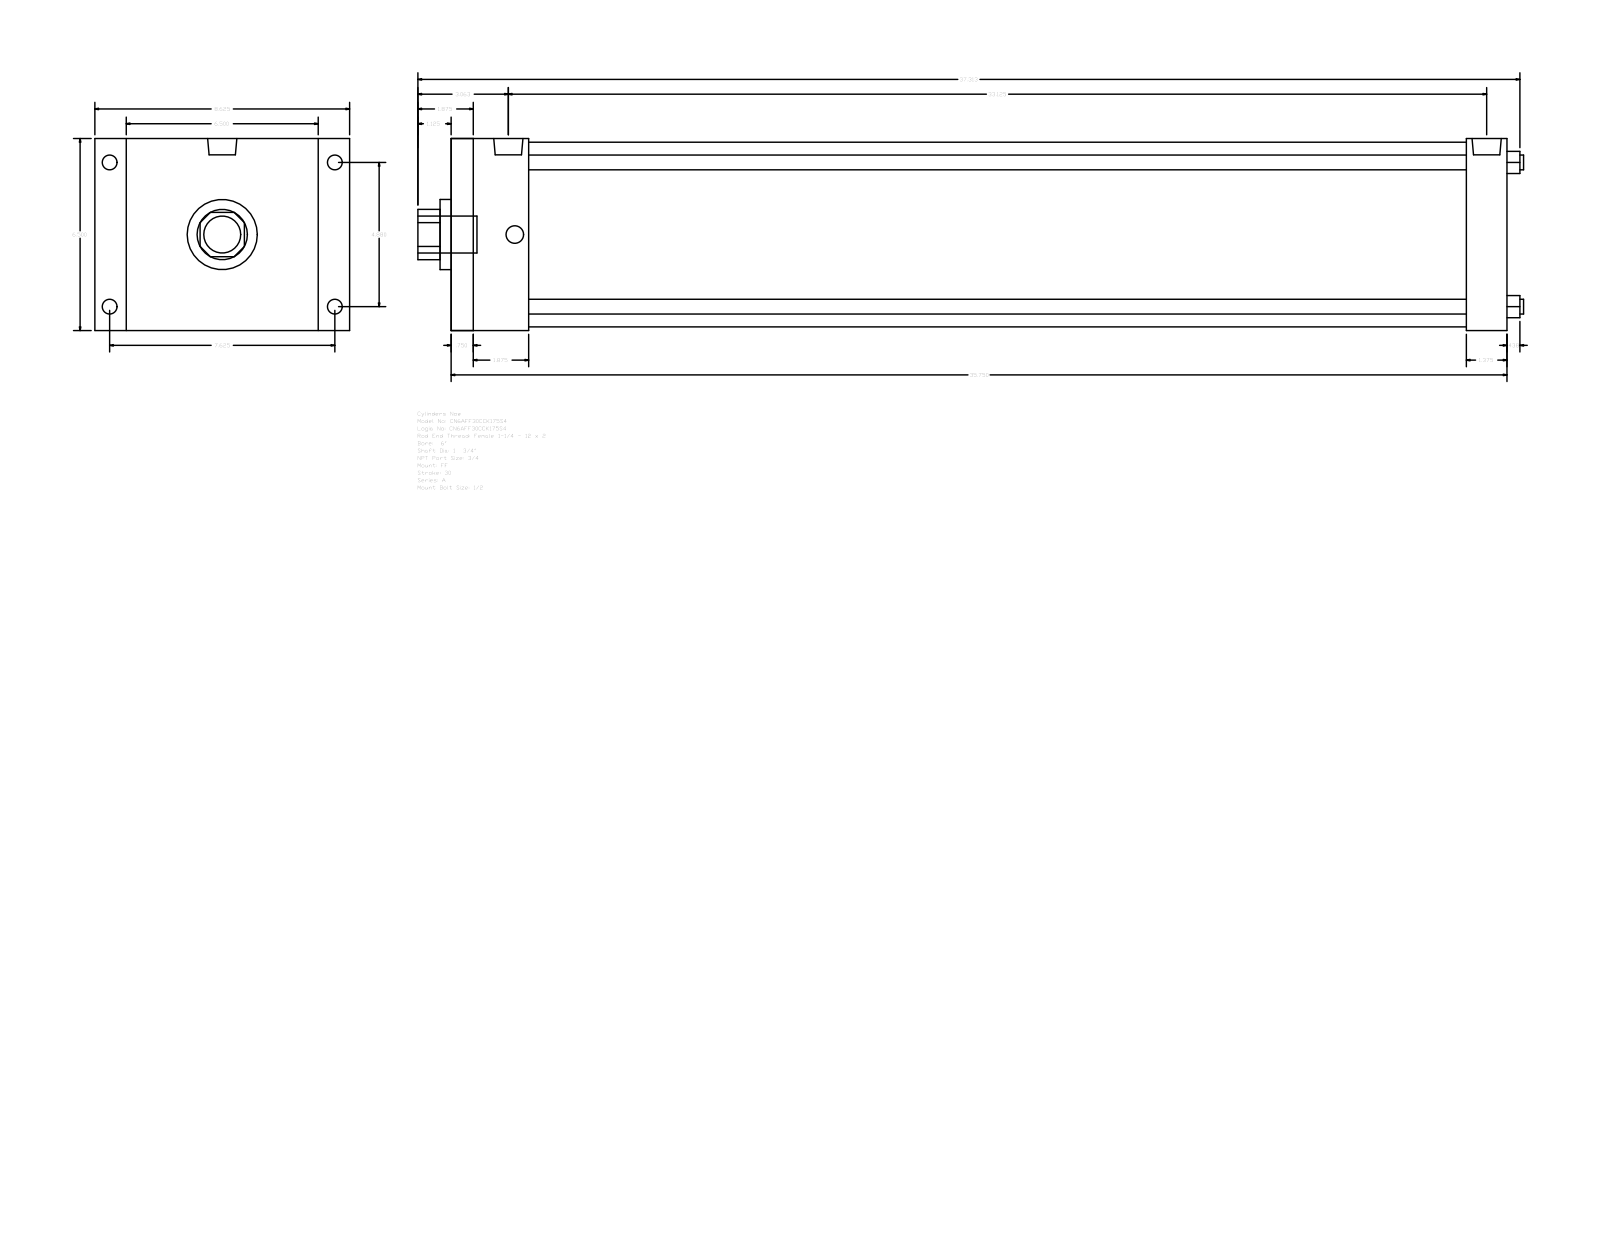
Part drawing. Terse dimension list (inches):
name: A_FF__0600_1.75
written by: GSSL Pune (CONFIG_CONTROL_DESIGN)
unit: in
bodies: 0 solids, 92 faces (64 planar, 28 cylindrical, 0 other)
size: 37.437 × 8.625 × 6.5
holes: 4× ⌀0.5, 1× ⌀1.75, 1× ⌀2.375, 1× ⌀6.25
bosses: 4× ⌀0.594, 4× ⌀0.5, 2× ⌀0.989, 1× ⌀1.25
rounds: 1× R0.852
face distances: 6.5, 35.75, 0.75, 35, 1.375, 2.625, 1.875, 33.125, 34.375, 33.625
hole spacings: 3.451, 4.88, 6.902
